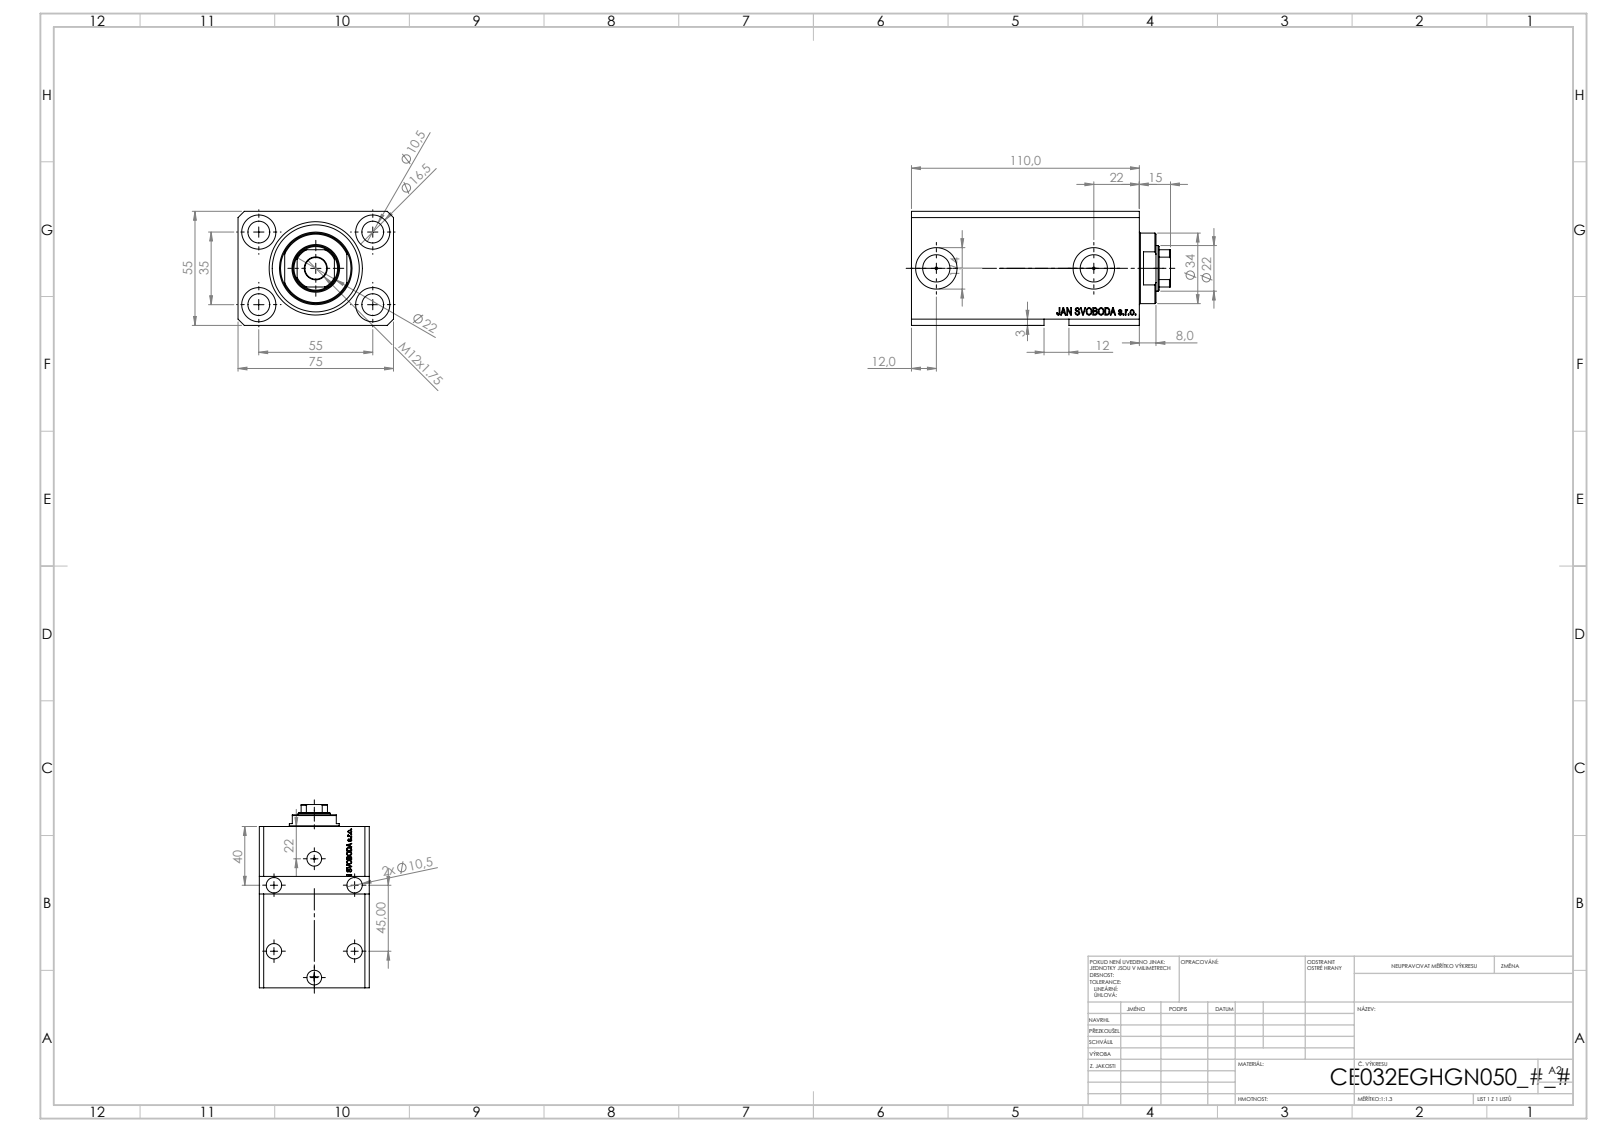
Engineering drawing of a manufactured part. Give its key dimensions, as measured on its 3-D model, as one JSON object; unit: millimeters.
{"part_name": "V250CE_VC_E; V250CE_E_Body; V250CE_C_VCP", "step_written_by": "SolidWorks 2019 (CONFIG_CONTROL_DESIGN)", "units": "millimeters", "bodies": {"solids": 3, "faces": 894, "planar": 438, "cylindrical": 84, "other": 372}, "overall_size": [124.9, 75, 55], "volume_mm3": 375529, "surface_area_mm2": 86474, "round_holes": [[10.5, 7], [1.25, 4], [16.5, 4], [10, 2], [13.16, 2], [20, 2], [22, 1], [32, 1], [45, 1]], "round_bosses_or_shafts": [[34, 1]], "partial_cylinders_radius": [[10.5, 1]], "face_to_face_distances": [55, 75, 110, 82.9, 27.1, 9.9, 73, 100.1, 11, 99], "hole_center_spacings": [32.6, 55, 32.87, 35, 65.19, 68.26, 68.74, 0.53]}
